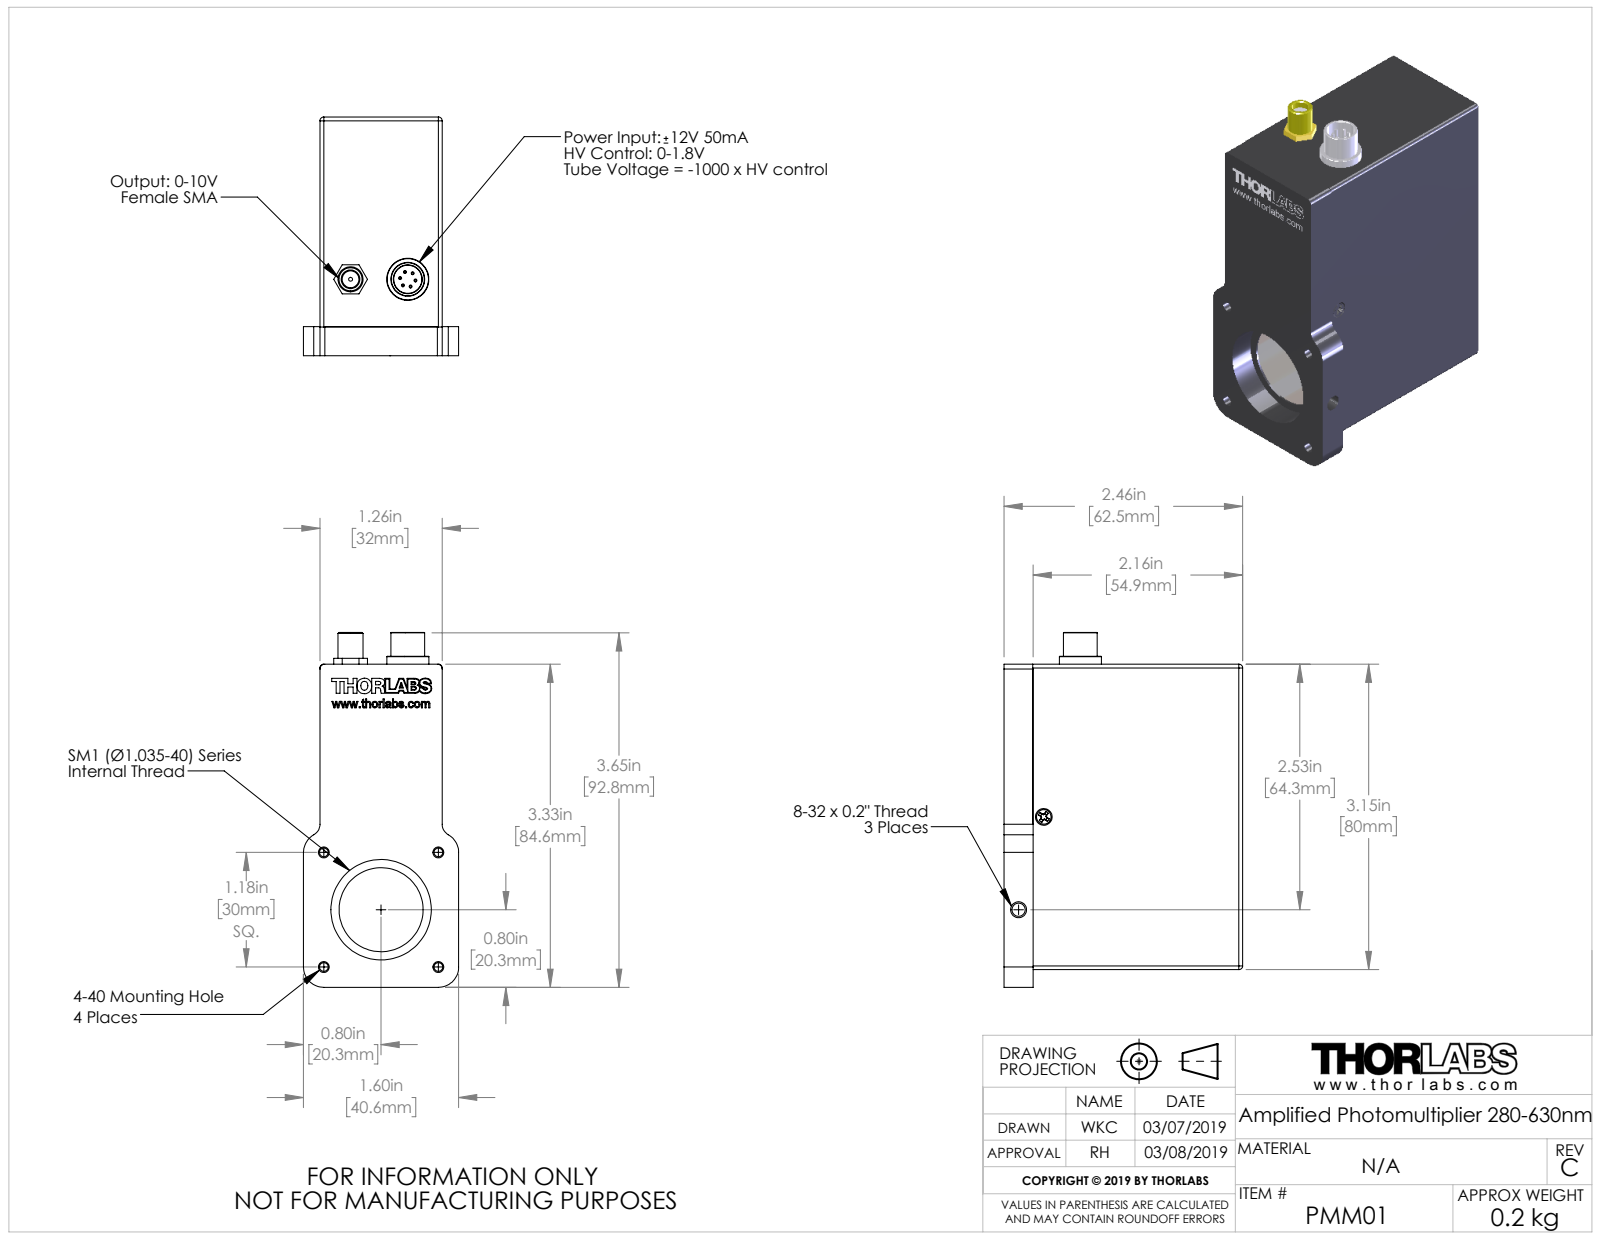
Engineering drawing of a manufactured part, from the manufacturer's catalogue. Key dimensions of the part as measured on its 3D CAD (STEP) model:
Part name (STEP PRODUCT): 17494-E0W
STEP written by: SolidWorks 2016 (AUTOMOTIVE_DESIGN)
Units: inches
Bodies: 0 solids, 241 faces (102 planar, 83 cylindrical, 56 other)
Overall size (bounding box): 3.658 × 2.46 × 1.6
Round holes (diameter × count): ⌀0.112 ×4, ⌀0.164 ×2, ⌀0.04 ×1, ⌀0.086 ×1, ⌀0.173 ×1, ⌀0.29 ×1, ⌀0.866 ×1, ⌀1.035 ×1, ⌀1.12 ×1
Round bosses / shafts (diameter × count): ⌀0.03 ×6, ⌀0.433 ×1, ⌀0.348 ×1, ⌀0.258 ×1, ⌀0.15 ×1, ⌀0.058 ×1
Partial cylindrical surfaces — rounded edges, fillets, slot ends (radius × count): R0.039 ×8, R0.209 ×4, R0.05 ×2, R0.125 ×2
Main face-to-face distances: 1.26, 2.461, 3.15, 0.045, 1.215, 2.161, 0.3, 0.035, 2.126, 0.335
Hole centre spacings: 0.835, 1.181, 1.67, 0.591, 0.694, 0.711, 0.991
